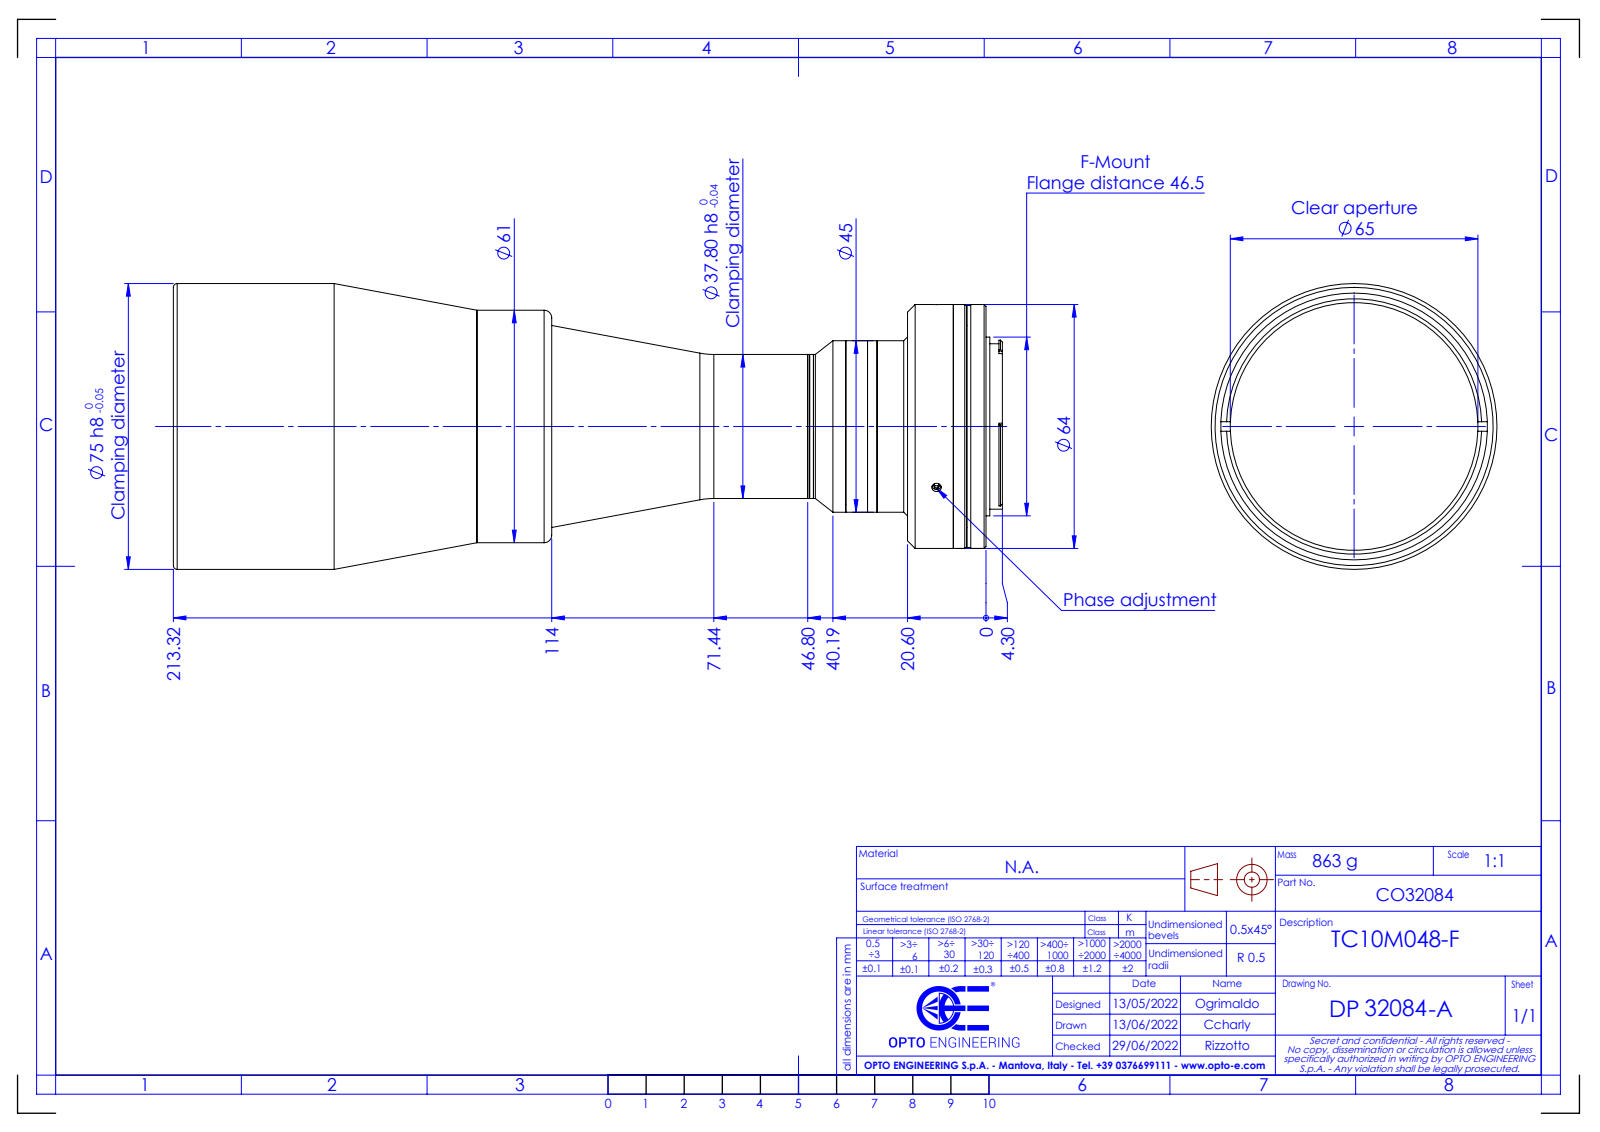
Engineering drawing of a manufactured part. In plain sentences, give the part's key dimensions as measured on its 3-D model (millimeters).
The part is named "DP32084-A_TC10M048-F". Its 3-D file was written by "SolidWorks 2021 (CONFIG_CONTROL_DESIGN)". It is 0 solids with 136 faces: 42 planar, 64 cylindrical and 30 other. Overall it measures 217.62 by 75 by 75 millimeters. Round holes: 3 of diameter 2.5, 1 of diameter 33, 1 of diameter 42, 1 of diameter 53, 1 of diameter 65, 1 of diameter 70. Round bosses or shafts: 1 of diameter 75, 1 of diameter 64, 1 of diameter 63.5, 1 of diameter 61, 1 of diameter 46.9, 1 of diameter 45, 1 of diameter 43.4, 1 of diameter 37.8. Partial cylindrical surfaces (rounded edges, fillets, slot ends): 5 of radius 0.5, 2 of radius 1.15, 1 of radius 22.65. The main face-to-face distances are 1, 5, 8.58, 3, 5.58, 12.02, 15.02, 20.6, 16.6, 4.58.
